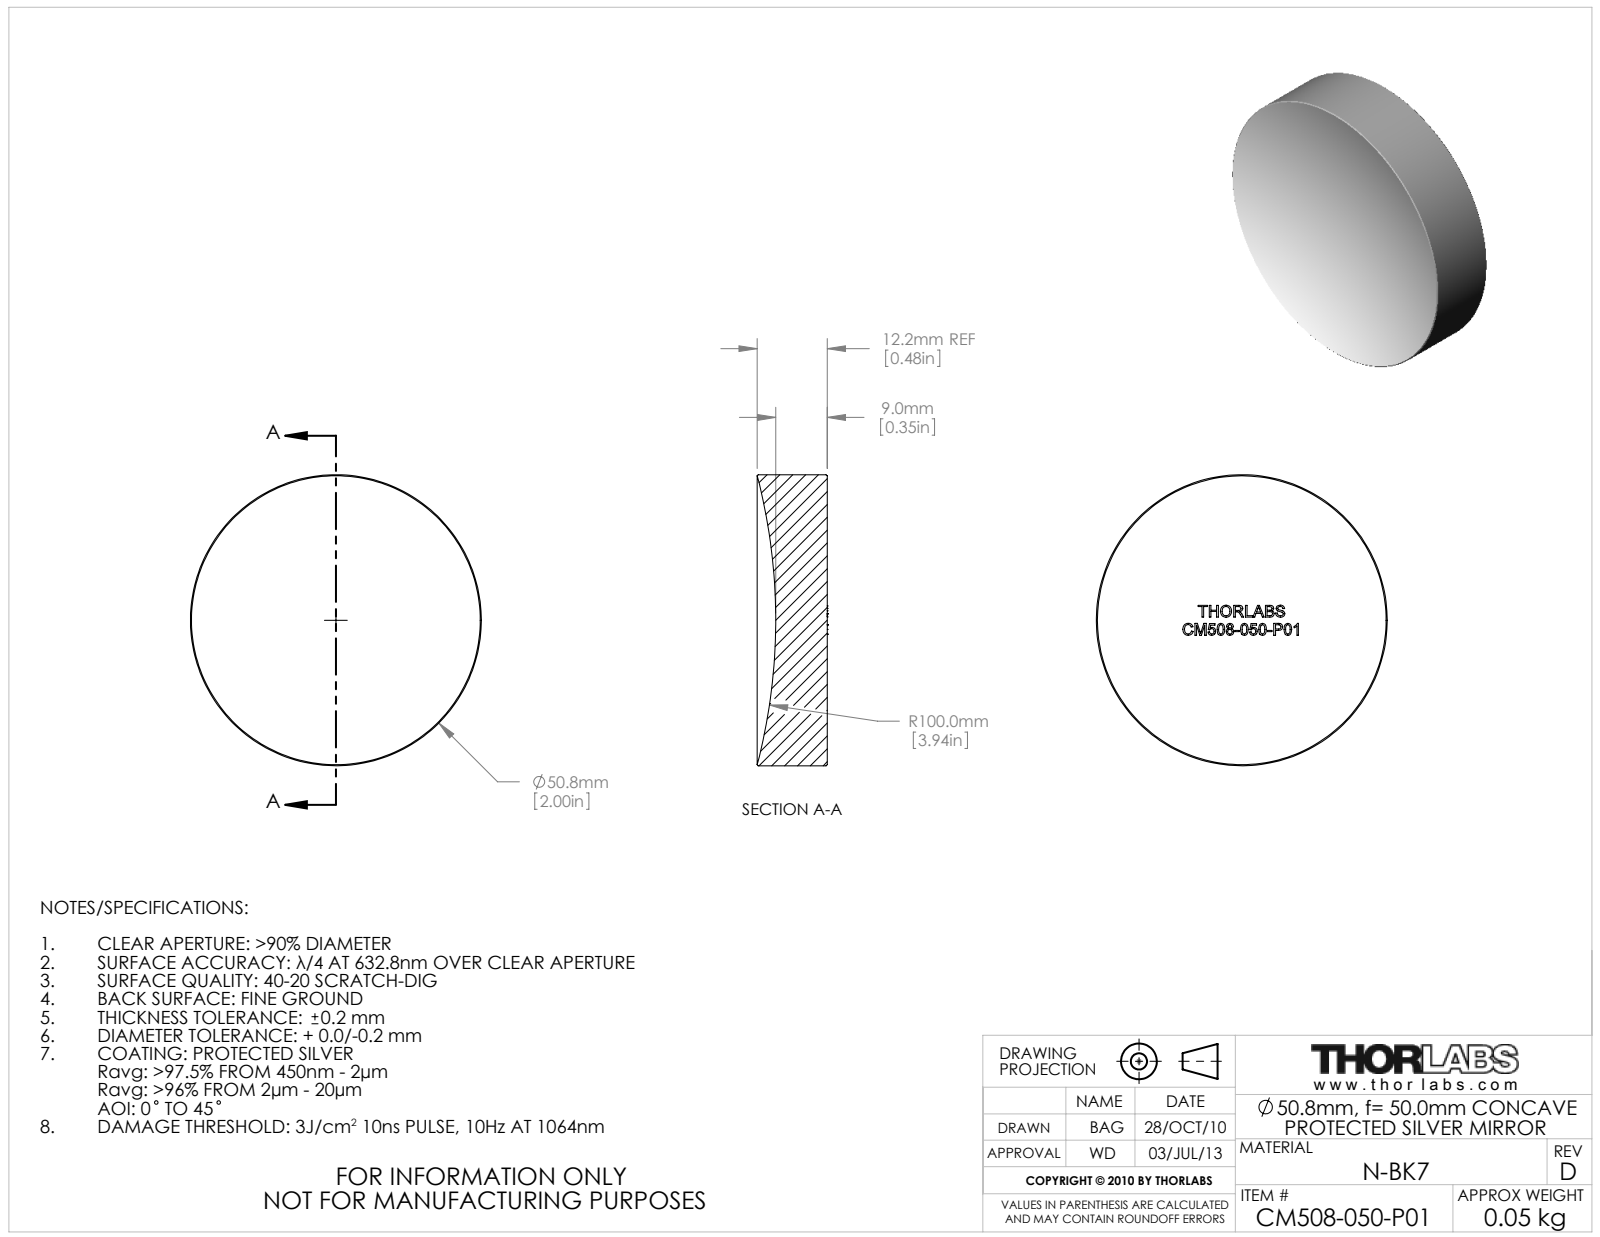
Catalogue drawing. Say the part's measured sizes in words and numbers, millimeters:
The part is named "17571-E0W". Its 3-D file was written by "SolidWorks 2012 (CONFIG_CONTROL_DESIGN)". It is 1 solid with 285 faces: 143 planar, 2 cylindrical and 140 other. Overall it measures 50.8 by 50.8 by 12.23 millimeters. Its volume is 21 540 cubic millimeters and its surface area 6 004 square millimeters. Round bosses or shafts: 1 of diameter 50.8. The main face-to-face distances are 2.56, 2.05, 7.14, 1.82, 2.32, 3.48, 2.06, 1.58, 1.76, 6.32.
